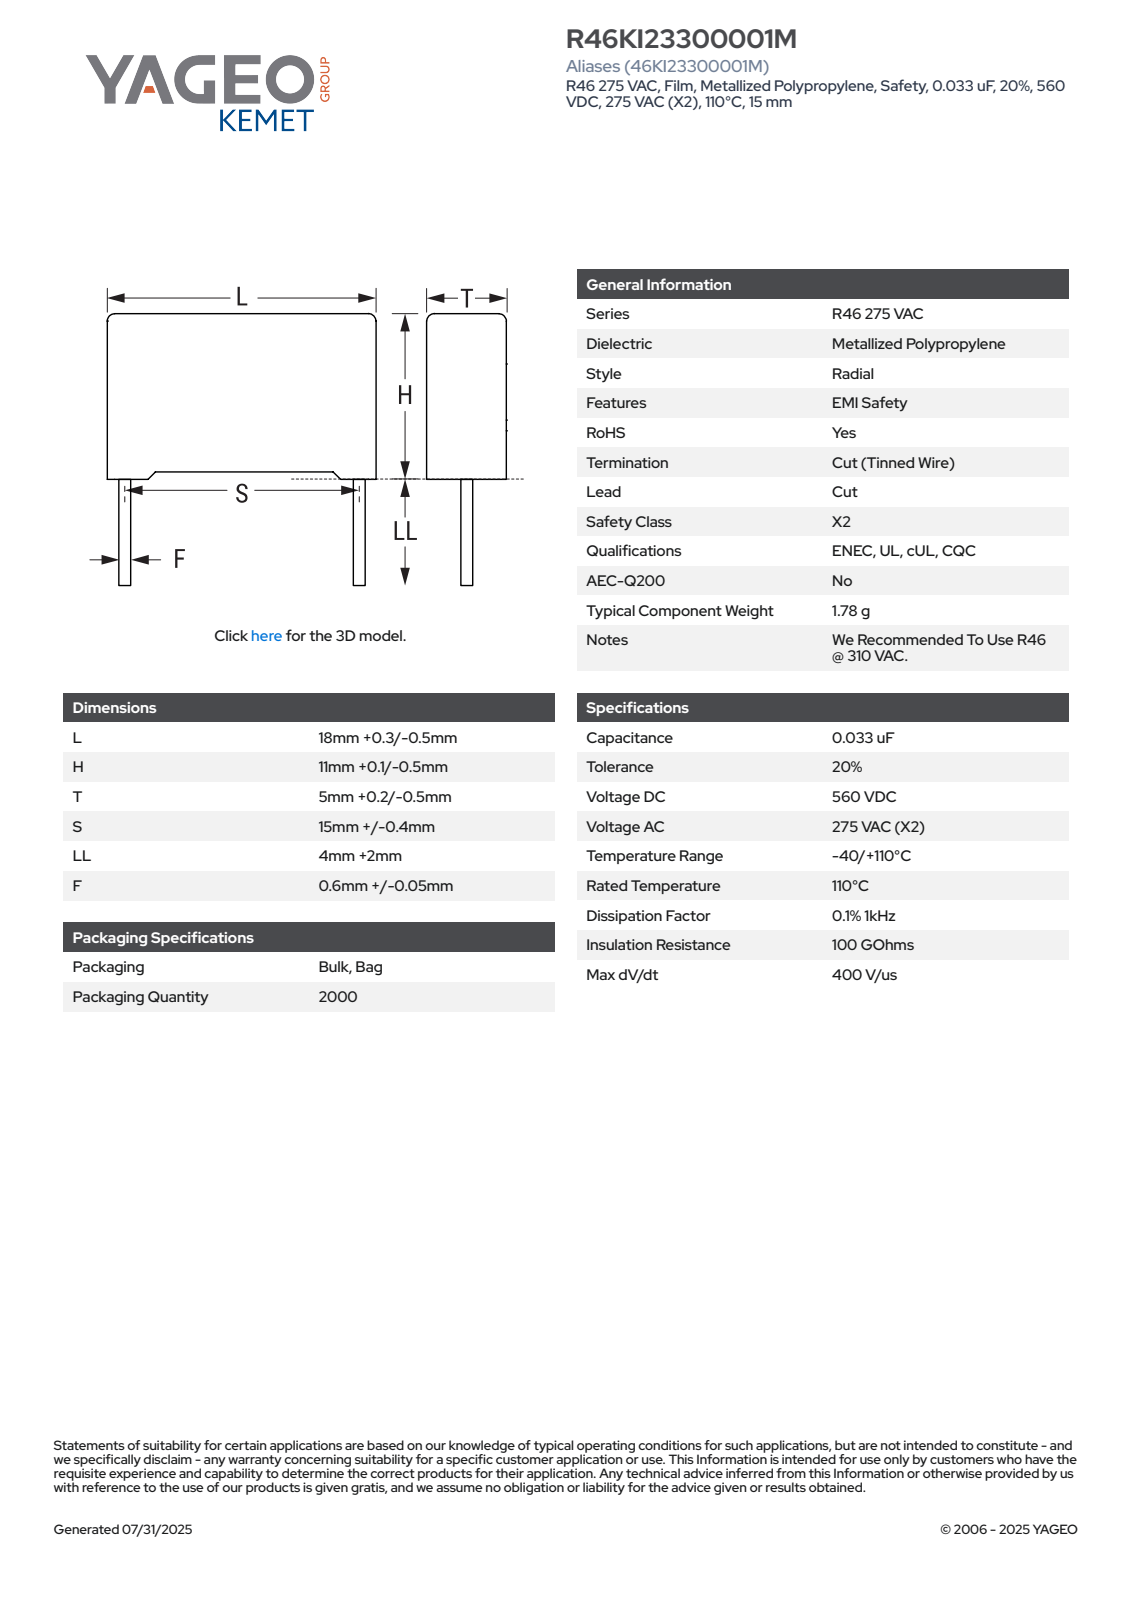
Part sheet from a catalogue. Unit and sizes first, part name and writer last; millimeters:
Units: millimetres
Overall size (bounding box): 18.3 × 17.1 × 5.21
Round bosses / shafts (diameter × count): ⌀0.65 ×2
Partial cylindrical surfaces — rounded edges, fillets, slot ends (radius × count): R0.5 ×4
Main face-to-face distances: 5.2, 10.35, 18.3, 0.61, 4.59, 0.37, 10.72, 0.38, 0.75, 11.1
Volume: 1 002 mm³ · Surface area: 769 mm²
Bodies: 4 solids, 85 faces (77 planar, 8 cylindrical, 0 other)
Part name (STEP PRODUCT): CFR_RB2_18X11X5_L18.3H11.1T5.2S15LL6F0.65
STEP written by: SolidWorks 2021 (AUTOMOTIVE_DESIGN)
